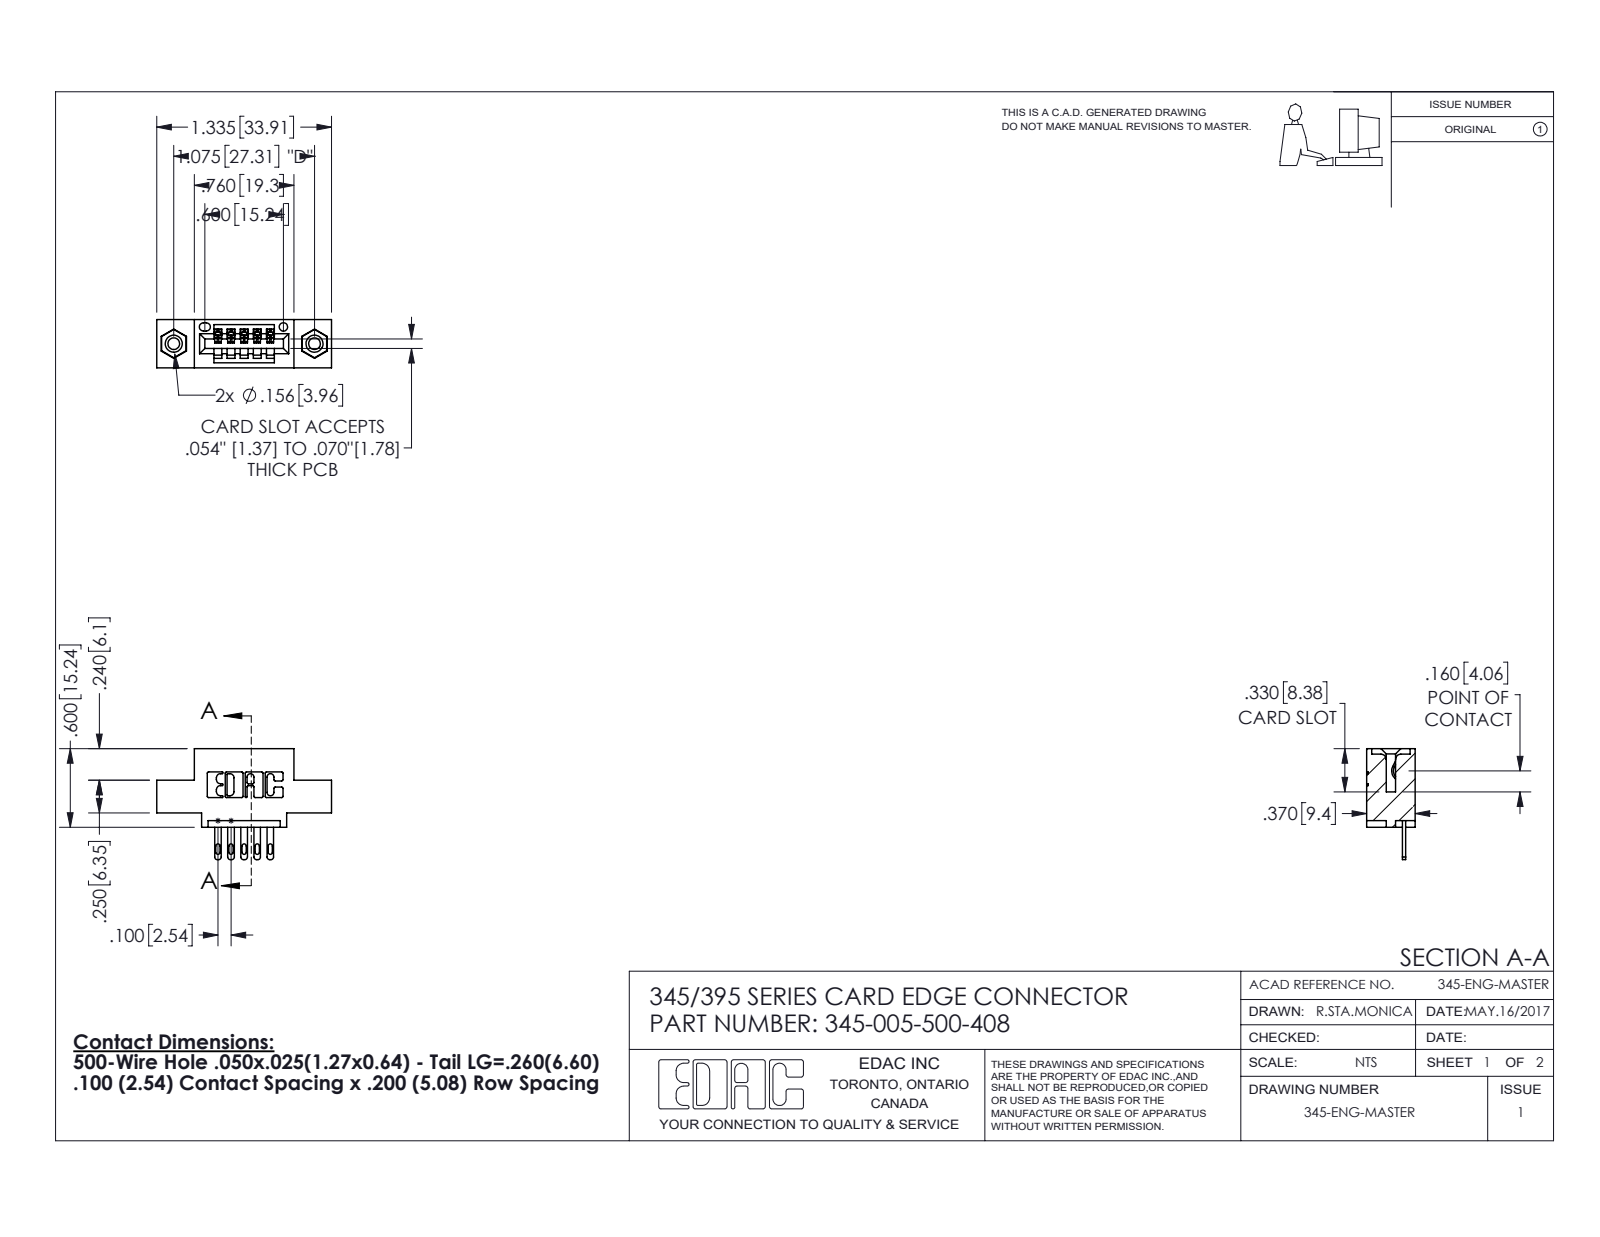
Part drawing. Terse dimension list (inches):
name: 345-250-001_345-250-003-102; 345-292-001_345-293-100; 345-005-500-408; 345 Part_0.110 Offset - 0.156 Dia-TI
written by: SolidWorks 2016 (CONFIG_CONTROL_DESIGN)
unit: in
bodies: 8 solids, 460 faces (286 planar, 158 cylindrical, 16 other)
size: 1.335 × 0.847 × 0.37
volume: 0.173 in³; area: 5.246 in²
holes: 2× ⌀0.089, 2× ⌀0.125, 2× ⌀0.156, 1× ⌀0.064
bosses: 2× ⌀0.155
rounds: 22× R0.01, 10× R0.006, 10× R0.016, 10× R0.02, 6× R0.007, 6× R0.031, 3× R0.026, 2× R0.031
face distances: 0.2, 0.37, 0.072, 0.298, 0.1, 0.025, 0.098, 0.272, 0.25, 0.06
hole spacings: 0.27, 0.847, 1.075
